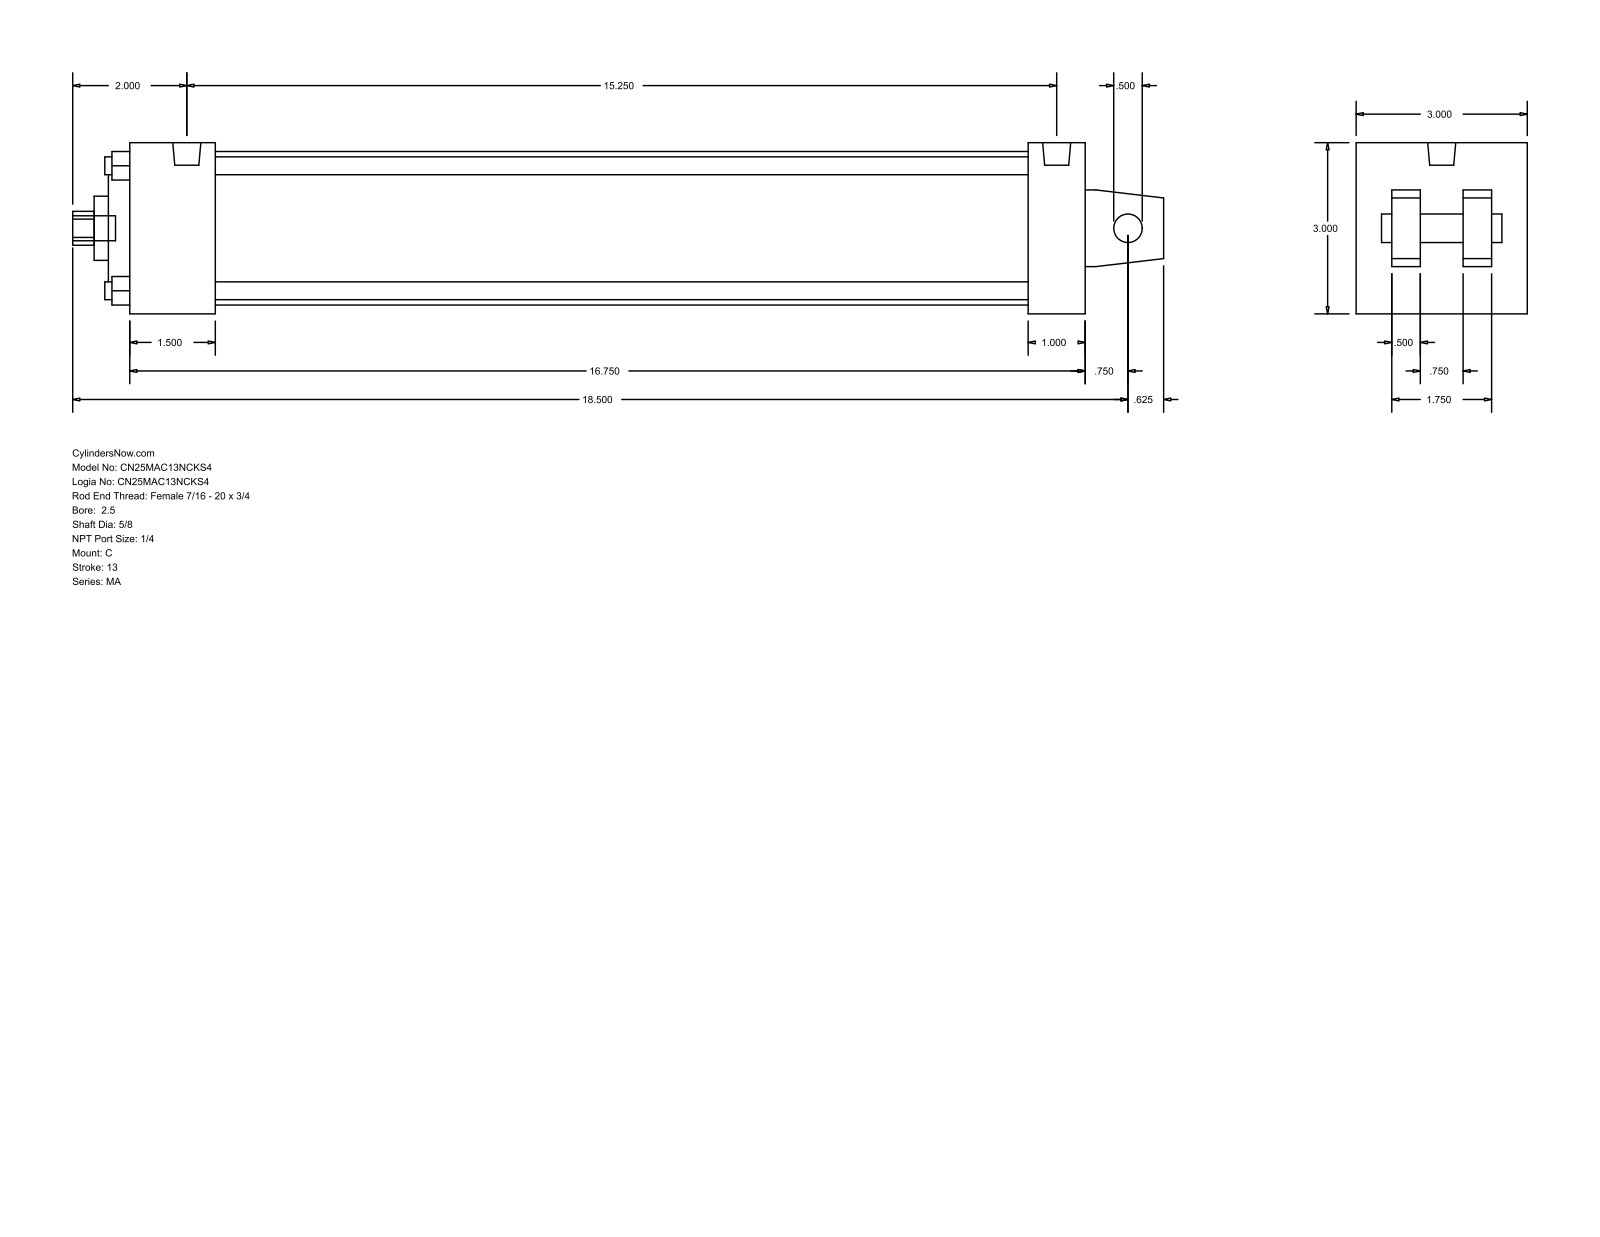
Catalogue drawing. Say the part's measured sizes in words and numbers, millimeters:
The part is named "MA_C__0250_0.625". Its 3-D file was written by "GSSL Pune (CONFIG_CONTROL_DESIGN)". It is 0 solids with 105 faces: 77 planar, 28 cylindrical and 0 other. Overall it measures 485.77 by 76.2 by 76.2 millimeters. Round holes: 4 of diameter 7.94, 1 of diameter 12.7, 1 of diameter 15.88, 1 of diameter 28.57, 1 of diameter 50.8, 1 of diameter 68.33. Round bosses or shafts: 4 of diameter 7.94, 2 of diameter 12.49, 1 of diameter 11.11. Partial cylindrical surfaces (rounded edges, fillets, slot ends): 1 of radius 7.54. The main face-to-face distances are 76.2, 425.45, 12.7, 15.87, 47.63, 25.4, 38.1, 400.05, 361.95, 387.35. The hole center spacings are 39.33, 55.62, 78.66.
